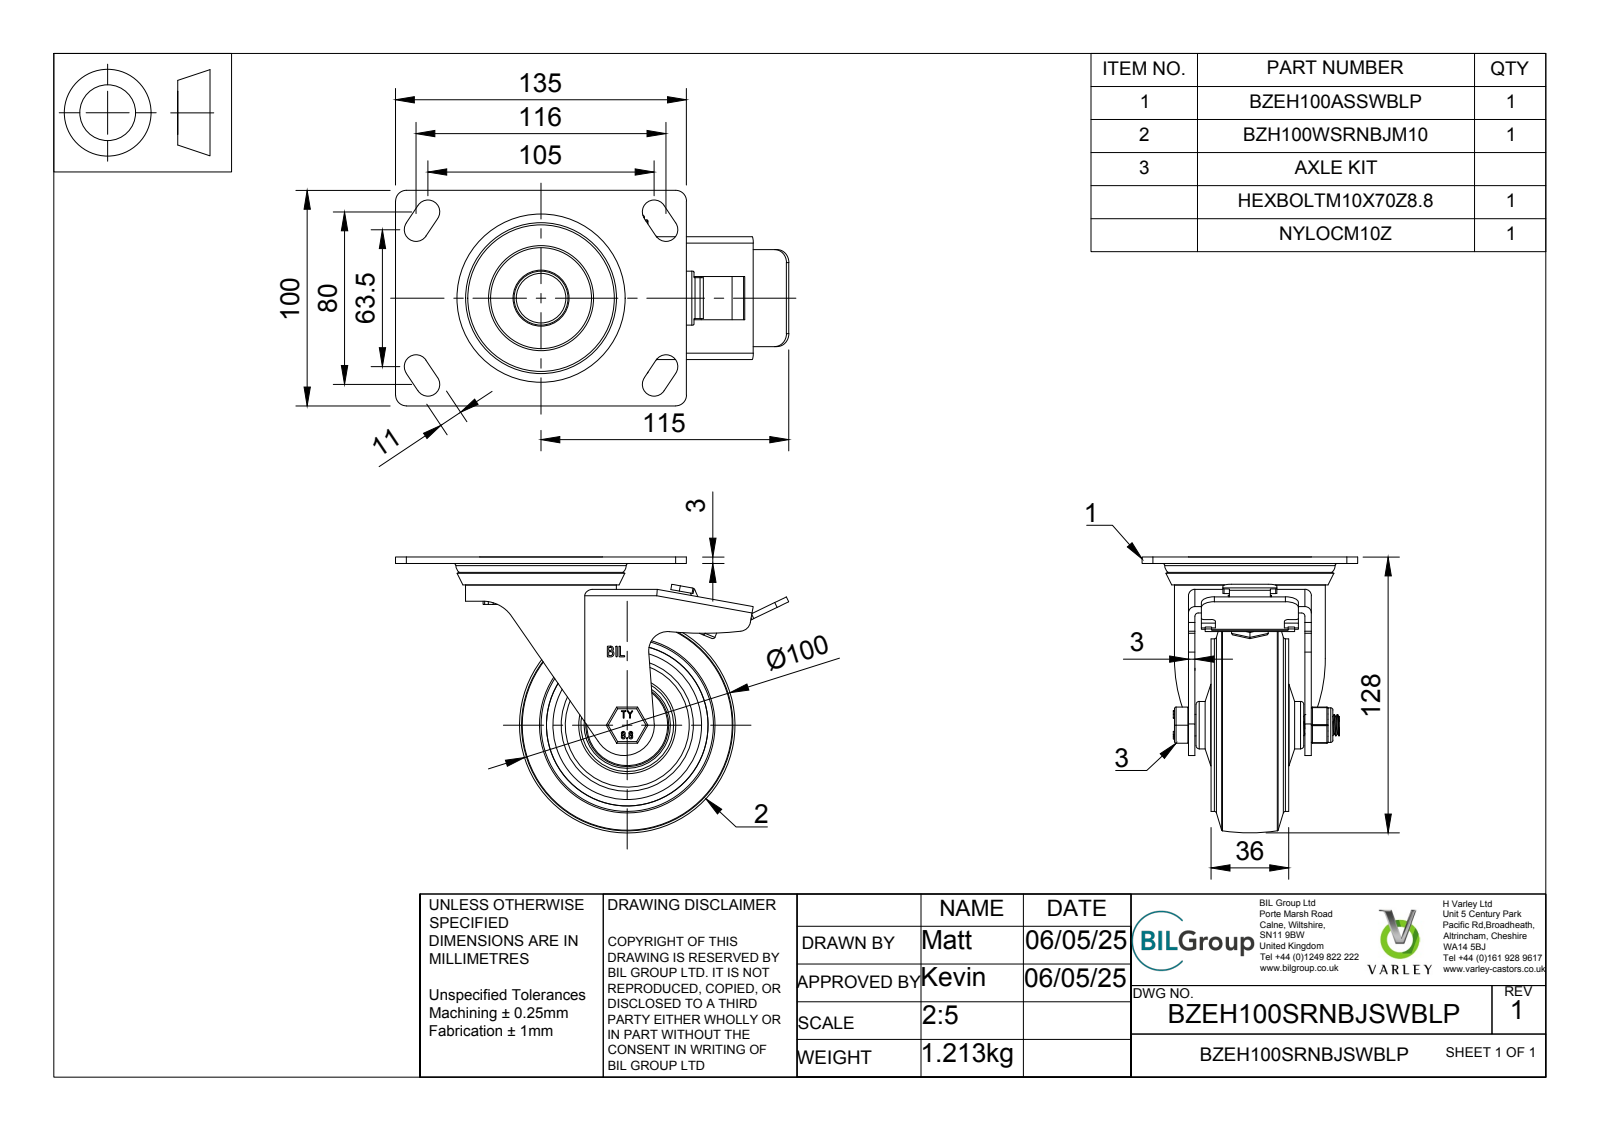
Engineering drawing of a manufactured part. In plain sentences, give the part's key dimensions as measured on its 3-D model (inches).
The part is named "BZEH100SRNBJSWBLP v3; BZEH100ASSWBLP v1; ZINC PLATED, PRESSED STEEL TOP PLATE; ZINC PLATED, PRESSED STEEL TOP PLATE Geometry (+7 more)". Its 3-D file was written by "Autodesk Translation Framework v14.4.0.0 (AUTOMOTIVE_DESIGN)". It is 46 solids with 984 faces: 458 planar, 210 cylindrical and 316 other. Overall it measures 7.185 by 5.039 by 3.937 inches. Its volume is 18.89 cubic inches and its surface area 257.6 square inches. Round holes: 2 of diameter 1.181, 1 of diameter 0.315, 1 of diameter 0.394, 1 of diameter 0.402, 1 of diameter 0.472, 1 of diameter 0.591, 1 of diameter 0.787, 1 of diameter 0.886, 1 of diameter 1.024, 1 of diameter 1.22, 1 of diameter 1.26, 1 of diameter 1.299. Round bosses or shafts: 1 of diameter 3.15, 1 of diameter 2.756, 1 of diameter 2.126, 1 of diameter 1.693, 1 of diameter 1.516, 1 of diameter 1.378, 1 of diameter 1.201, 1 of diameter 1.102. Partial cylindrical surfaces (rounded edges, fillets, slot ends): 20 of radius 0.02, 8 of radius 0.039, 8 of radius 0.217, 6 of radius 0.03, 6 of radius 0.059, 5 of radius 0.197, 4 of radius 0.118, 3 of radius 0.079. The main face-to-face distances are 0.118, 0.197, 0.079, 0.394, 0.039, 2.126, 0.591, 0.276, 0.315, 0.512.
